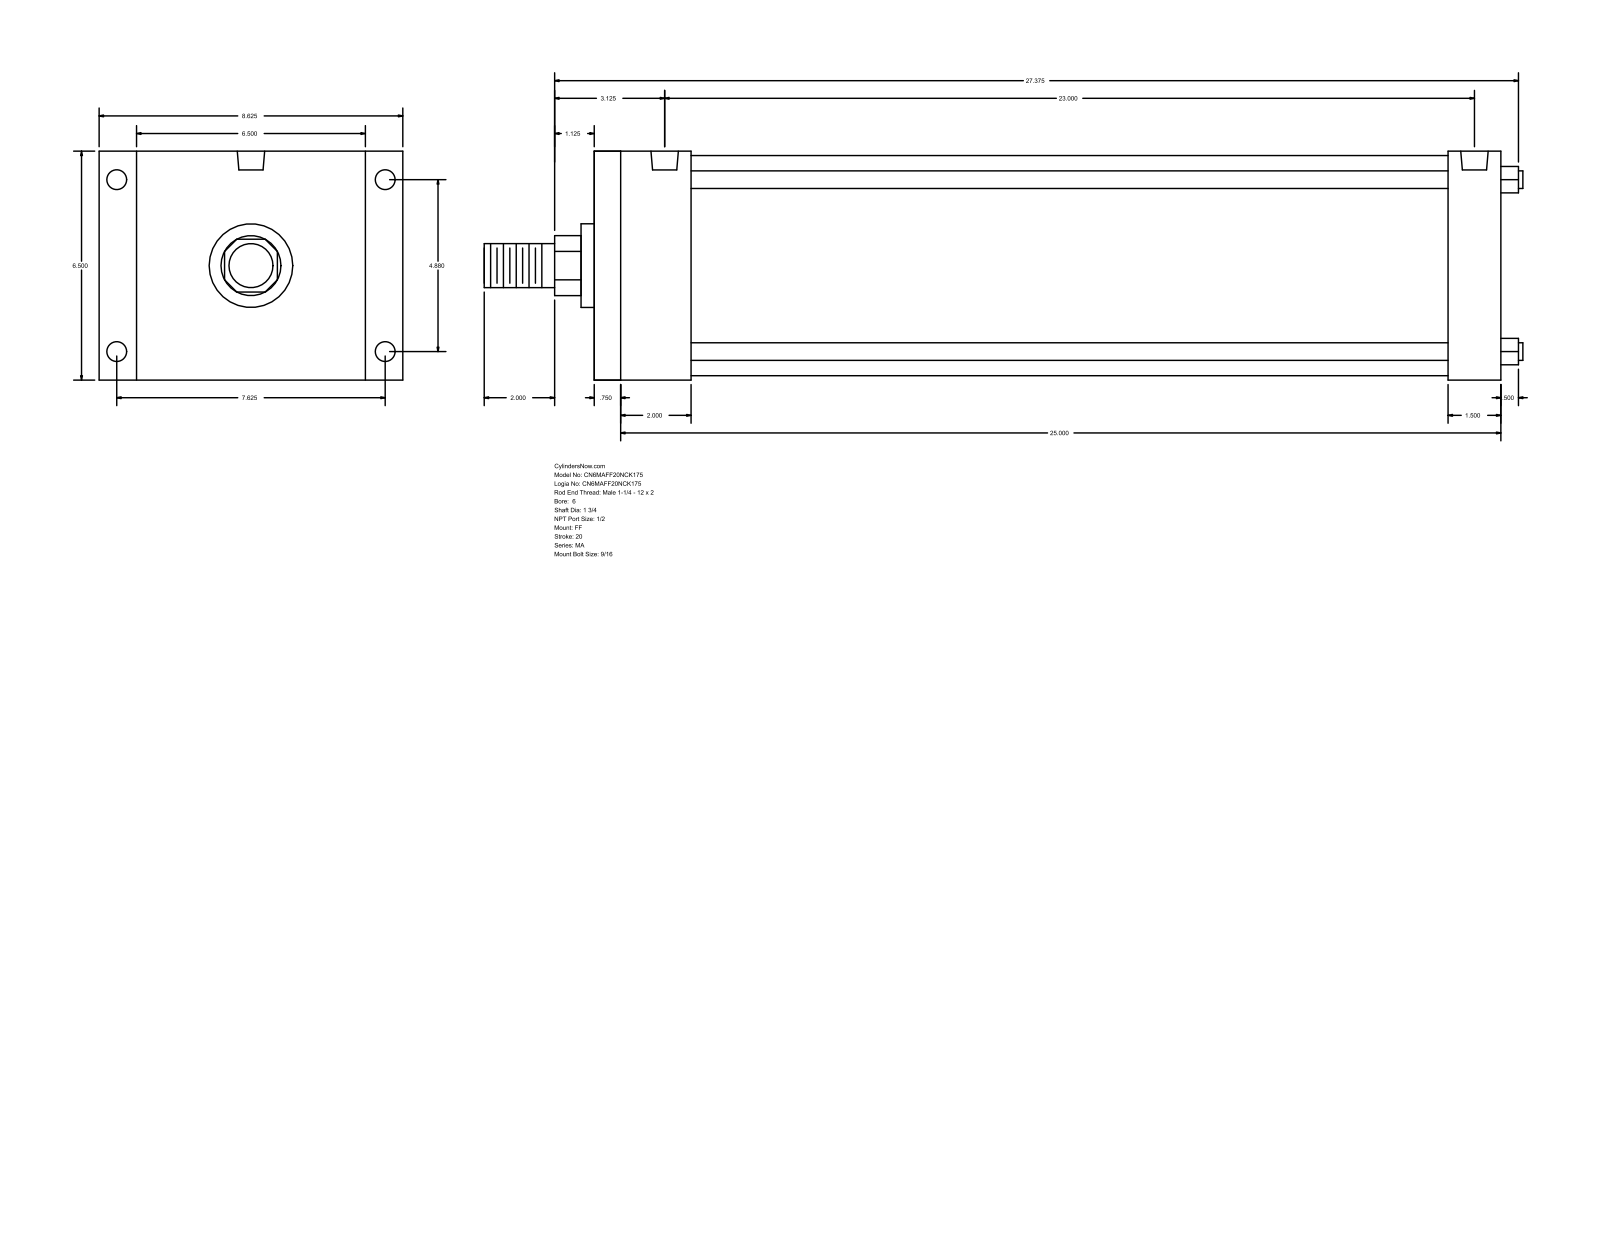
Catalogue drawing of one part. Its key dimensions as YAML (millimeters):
part_name: "MA_FF__0600_1.75"
step_written_by: "GSSL Pune (CONFIG_CONTROL_DESIGN)"
units: millimeters
bodies: {solids: 0, faces: 92, planar: 64, cylindrical: 28, other: 0}
overall_size: [749.3, 219.07, 165.1]
round_holes:
  - {diameter: 14.29, count: 4}
  - {diameter: 17.46, count: 4}
  - {diameter: 19.77, count: 2}
round_bosses_or_shafts:
  - {diameter: 12.7, count: 4}
  - {diameter: 158.75, count: 1}
  - {diameter: 60.33, count: 1}
  - {diameter: 44.45, count: 1}
  - {diameter: 31.75, count: 1}
partial_cylinders:
  - {radius: 21.63, count: 1}
face_to_face_distances: [165.1, 654.05, 19.05, 635, 69.85, 38.1, 50.8, 584.2, 615.95, 596.9]
hole_center_spacings: [123.96, 193.68, 229.95, 584.2]
